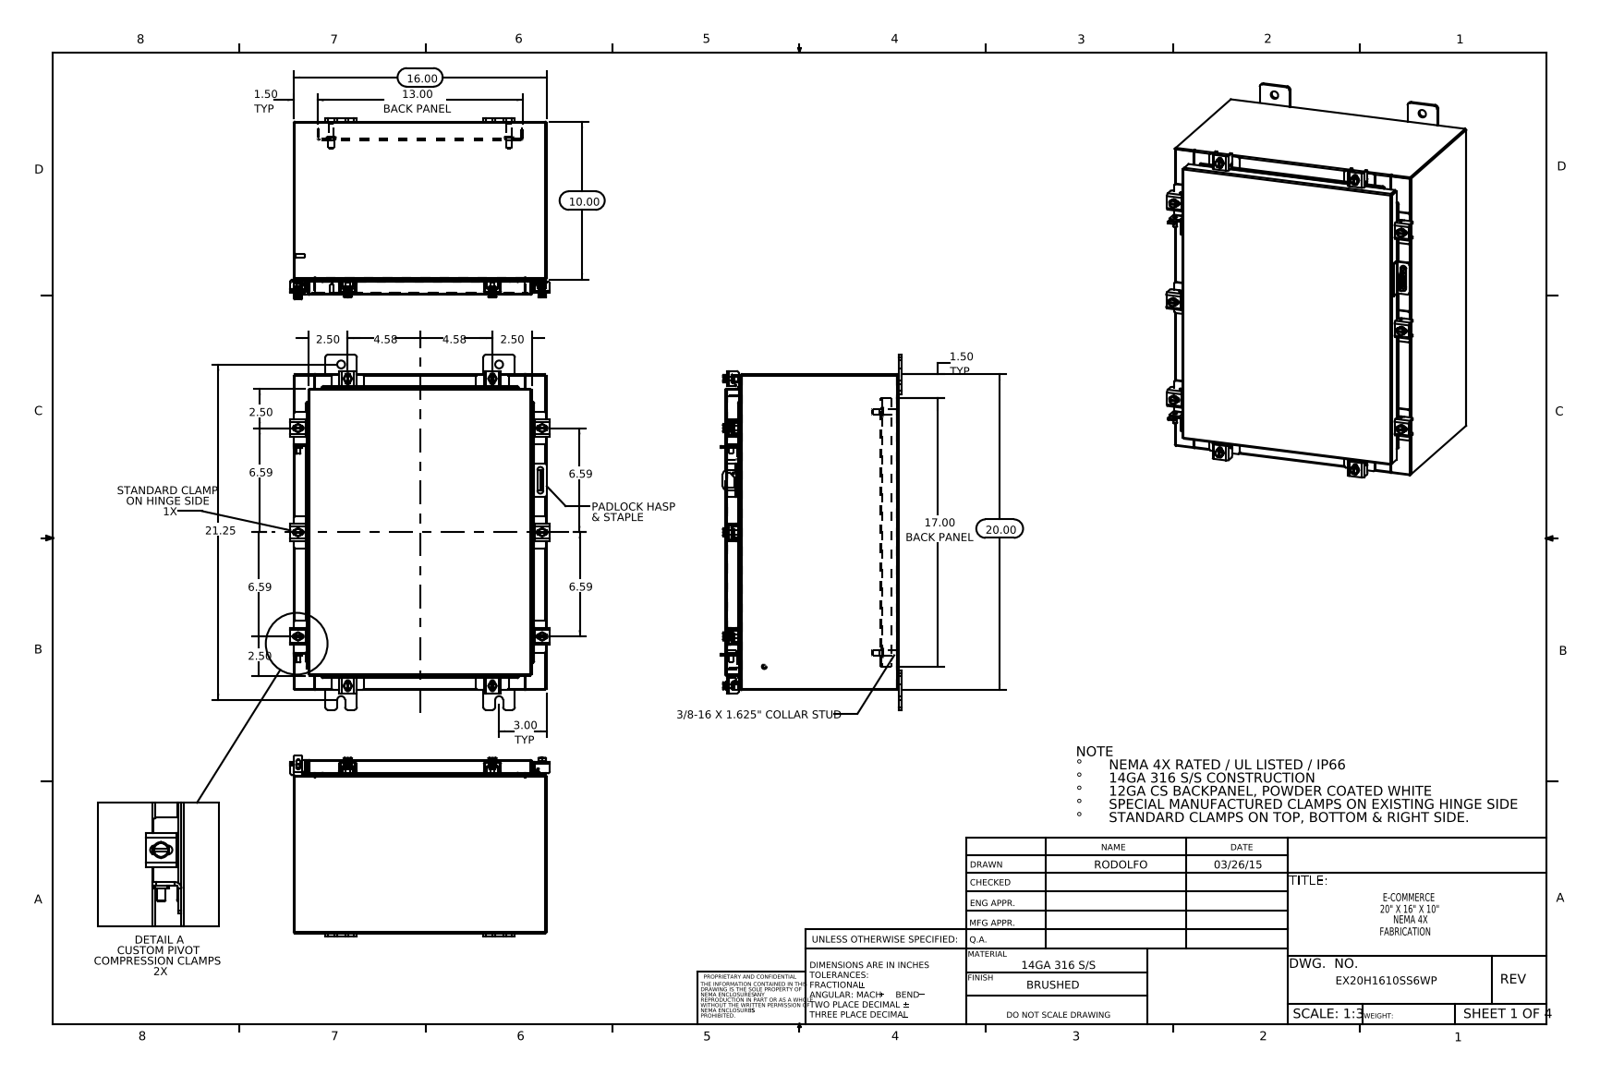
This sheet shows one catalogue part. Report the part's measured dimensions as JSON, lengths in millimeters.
{"part_name": "HW-CLN-NH-20330; EX20H1610SS6WP Backpanel; 30X10 Clamp Bracket2; 22104005_DEFAULT_RTP30 (+8 more)", "step_written_by": "SolidWorks 2014 (CONFIG_CONTROL_DESIGN)", "units": "millimeters", "bodies": {"solids": 71, "faces": 1784, "planar": 955, "cylindrical": 685, "other": 144}, "overall_size": [571.5, 417.1, 290.9], "volume_mm3": 2394000, "surface_area_mm2": 2382000, "round_holes": [[5.4, 10], [6.6, 10], [12.7, 8], [3.2, 1], [6.4, 1]], "round_bosses_or_shafts": [[12.7, 10], [6.4, 10], [10.1, 8], [15.9, 4], [9.5, 4], [8.4, 4], [8, 2], [6, 2]], "partial_cylinders_radius": [[1.5, 46], [0.3, 24], [4.8, 24], [2.2, 22], [3.6, 20], [3, 18], [2.3, 16], [2.5, 16]], "face_to_face_distances": [1.9, 276.9, 404.5, 506.1, 278.8, 275, 2.6, 25.4, 27.3, 249.6], "hole_center_spacings": [59.6, 112.8, 167.5, 259.6, 322.5, 365.1, 398.3, 422.1]}
